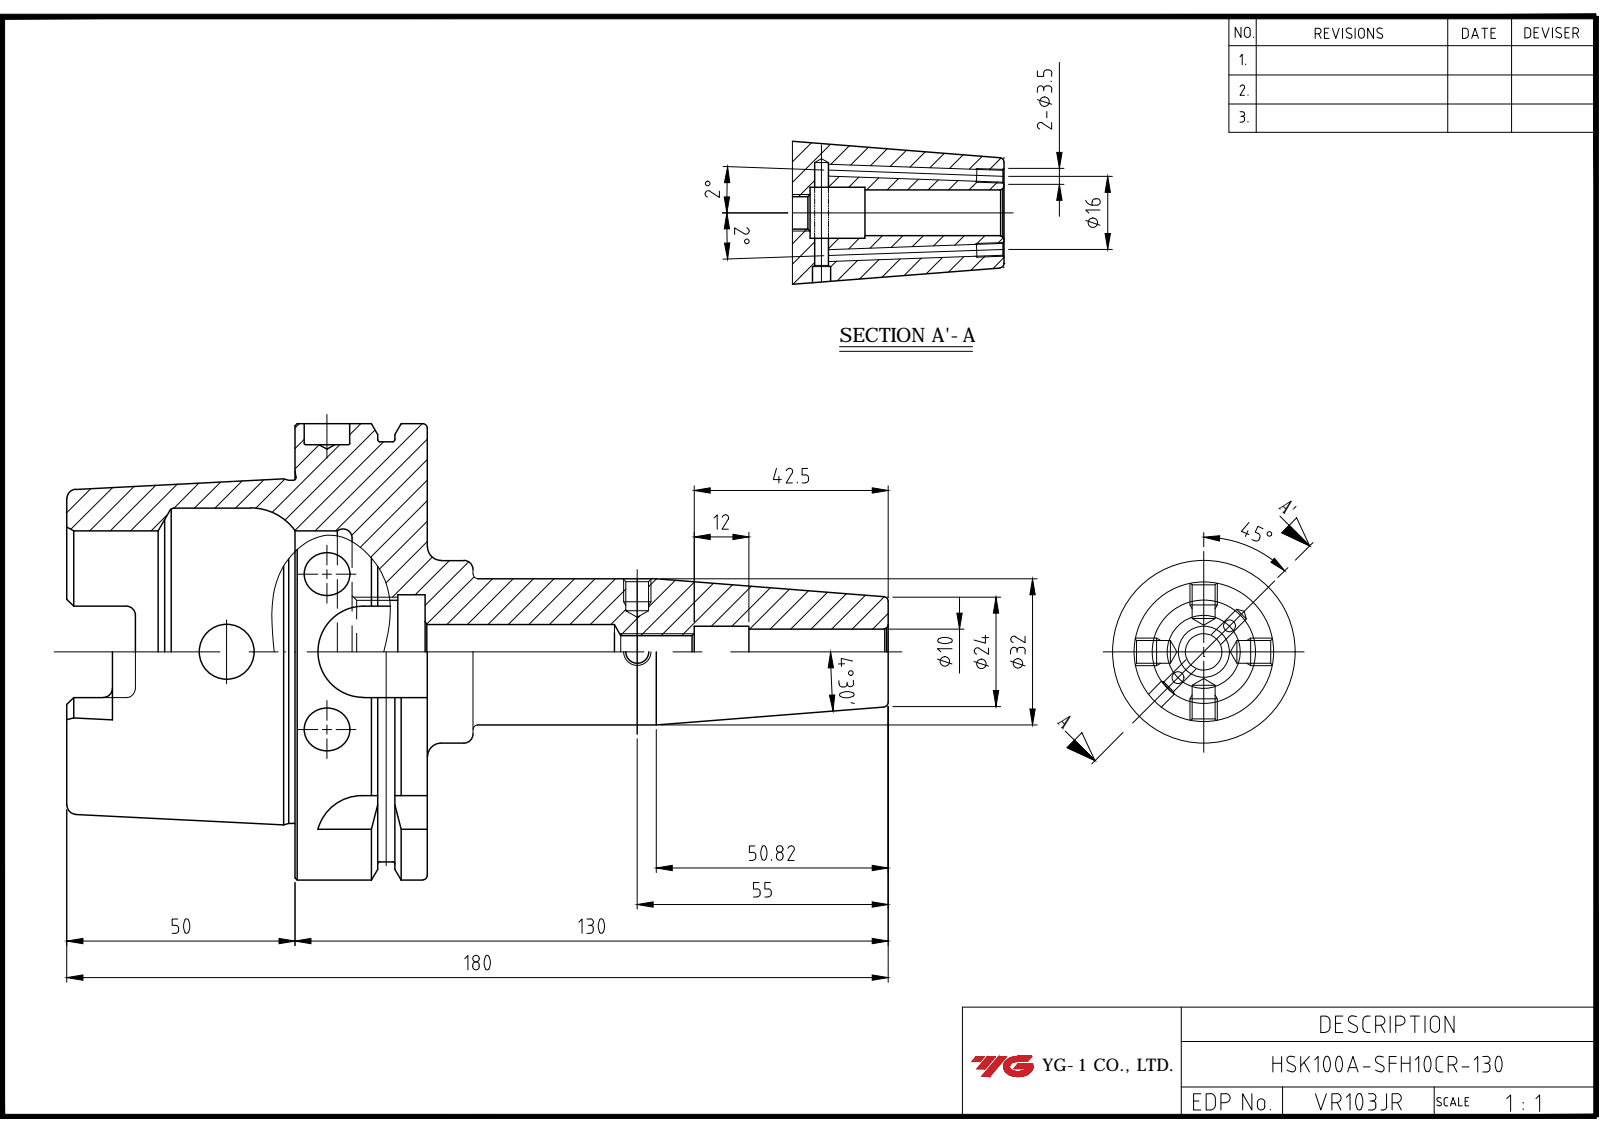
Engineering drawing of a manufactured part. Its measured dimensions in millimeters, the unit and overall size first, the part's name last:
Units: millimetres
Overall size (bounding box): 180 × 100 × 100
Round holes (diameter × count): ⌀2.46 ×2, ⌀10 ×2, ⌀12 ×2, ⌀6.92 ×1, ⌀11.2 ×1, ⌀22.38 ×1, ⌀25 ×1, ⌀53 ×1, ⌀63 ×1
Round bosses / shafts (diameter × count): ⌀100 ×1, ⌀92 ×1, ⌀75.41 ×1, ⌀40 ×1, ⌀32 ×1
Partial cylindrical surfaces — rounded edges, fillets, slot ends (radius × count): R2 ×6, R4.88 ×4, R10 ×4
Main face-to-face distances: 29, 12.5, 16.5, 62.5, 50, 79, 88, 78.5, 28.5, 16
Volume: 321 473 mm³ · Surface area: 62 521 mm²
Bodies: 1 solid, 123 faces (38 planar, 38 cylindrical, 47 other)
Part name (STEP PRODUCT): LO-HSK100A-SFH10CR-130
STEP written by: Autodesk Inventor 2024 (AUTOMOTIVE_DESIGN)
